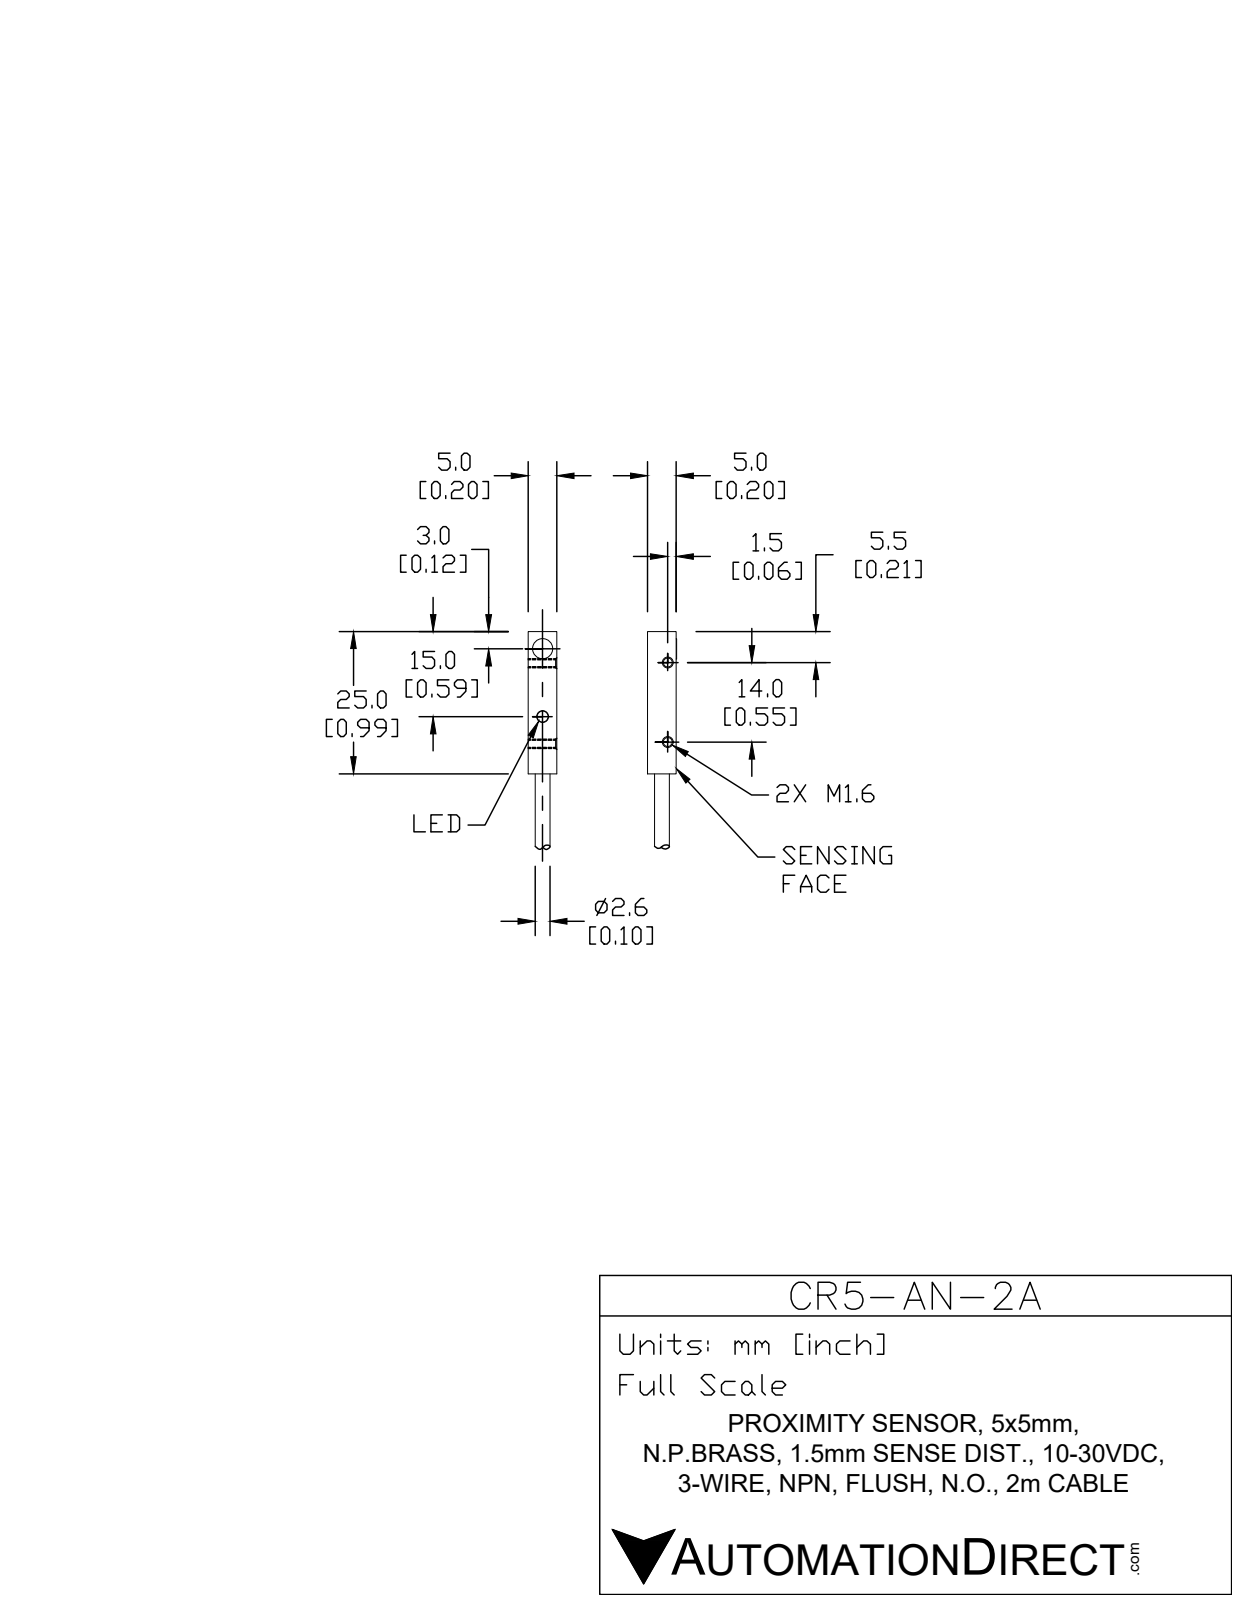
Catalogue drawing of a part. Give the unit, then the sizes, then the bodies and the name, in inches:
Units: inches
Overall size (bounding box): 1.772 × 0.197 × 0.197
Round holes (diameter × count): ⌀0.048 ×2, ⌀0.039 ×1, ⌀0.102 ×1
Round bosses / shafts (diameter × count): ⌀0.102 ×1
Main face-to-face distances: 0.197, 0.984, 0.187, 0.787, 1.772
Hole centre spacings: 0.472, 0.551
Volume: 0.044 in³ · Surface area: 1.162 in²
Bodies: 1 solid, 18 faces (8 planar, 5 cylindrical, 5 other)
Part name (STEP PRODUCT): CR5-AN-2A
STEP written by: SolidWorks 2017 (AUTOMOTIVE_DESIGN)
